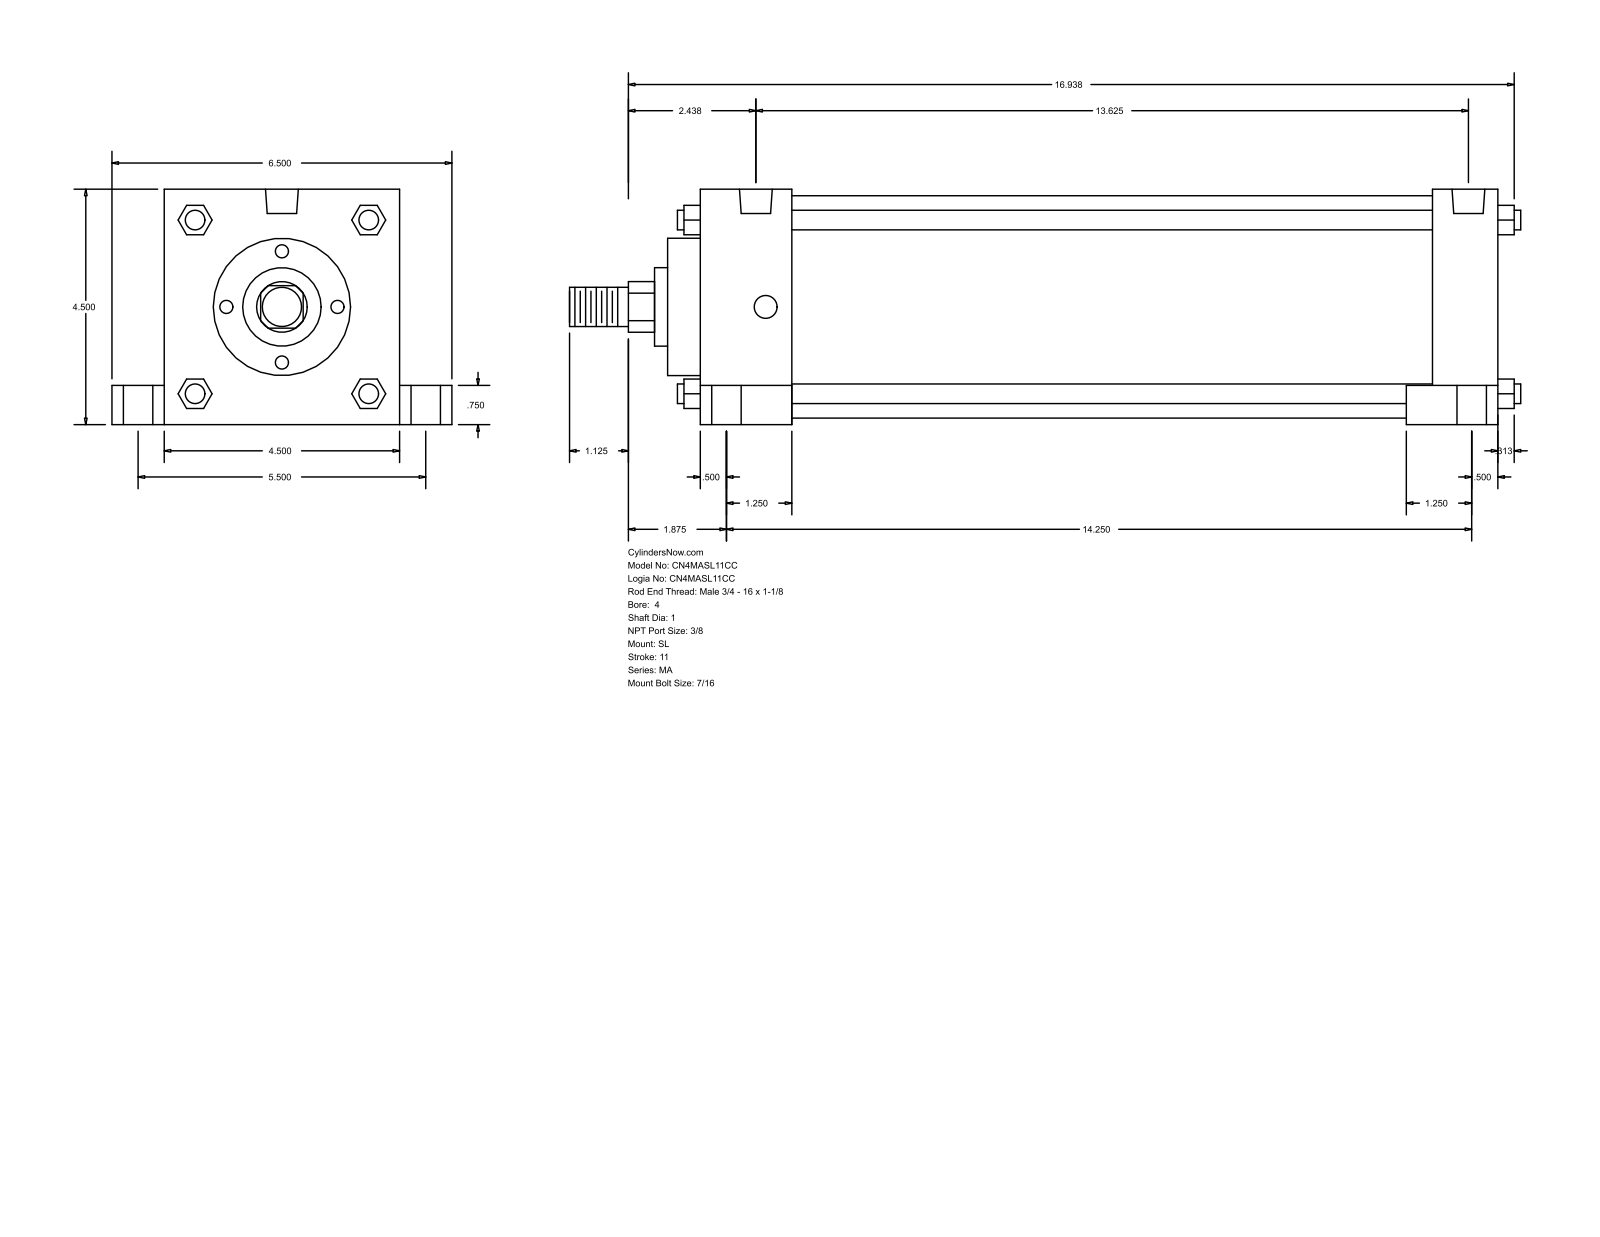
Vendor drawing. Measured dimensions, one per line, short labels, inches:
name: MA_SL__0400_1
written by: GSSL Pune (CONFIG_CONTROL_DESIGN)
unit: in
bodies: 0 solids, 150 faces (113 planar, 37 cylindrical, 0 other)
size: 18.187 × 6.5 × 4.5
holes: 4× ⌀0.437, 4× ⌀0.563, 4× ⌀0.813, 2× ⌀0.627
bosses: 4× ⌀0.375, 1× ⌀4.25, 1× ⌀2.625, 1× ⌀1.5, 1× ⌀1, 1× ⌀0.75
rounds: 1× R0.484
face distances: 4.5, 15.25, 1.75, 13.5, 14, 12.25, 1.25, 1, 5.5, 15.875
hole spacings: 0.187, 2.751, 2.761, 2.807, 2.85, 5.5, 13.25, 13.438
